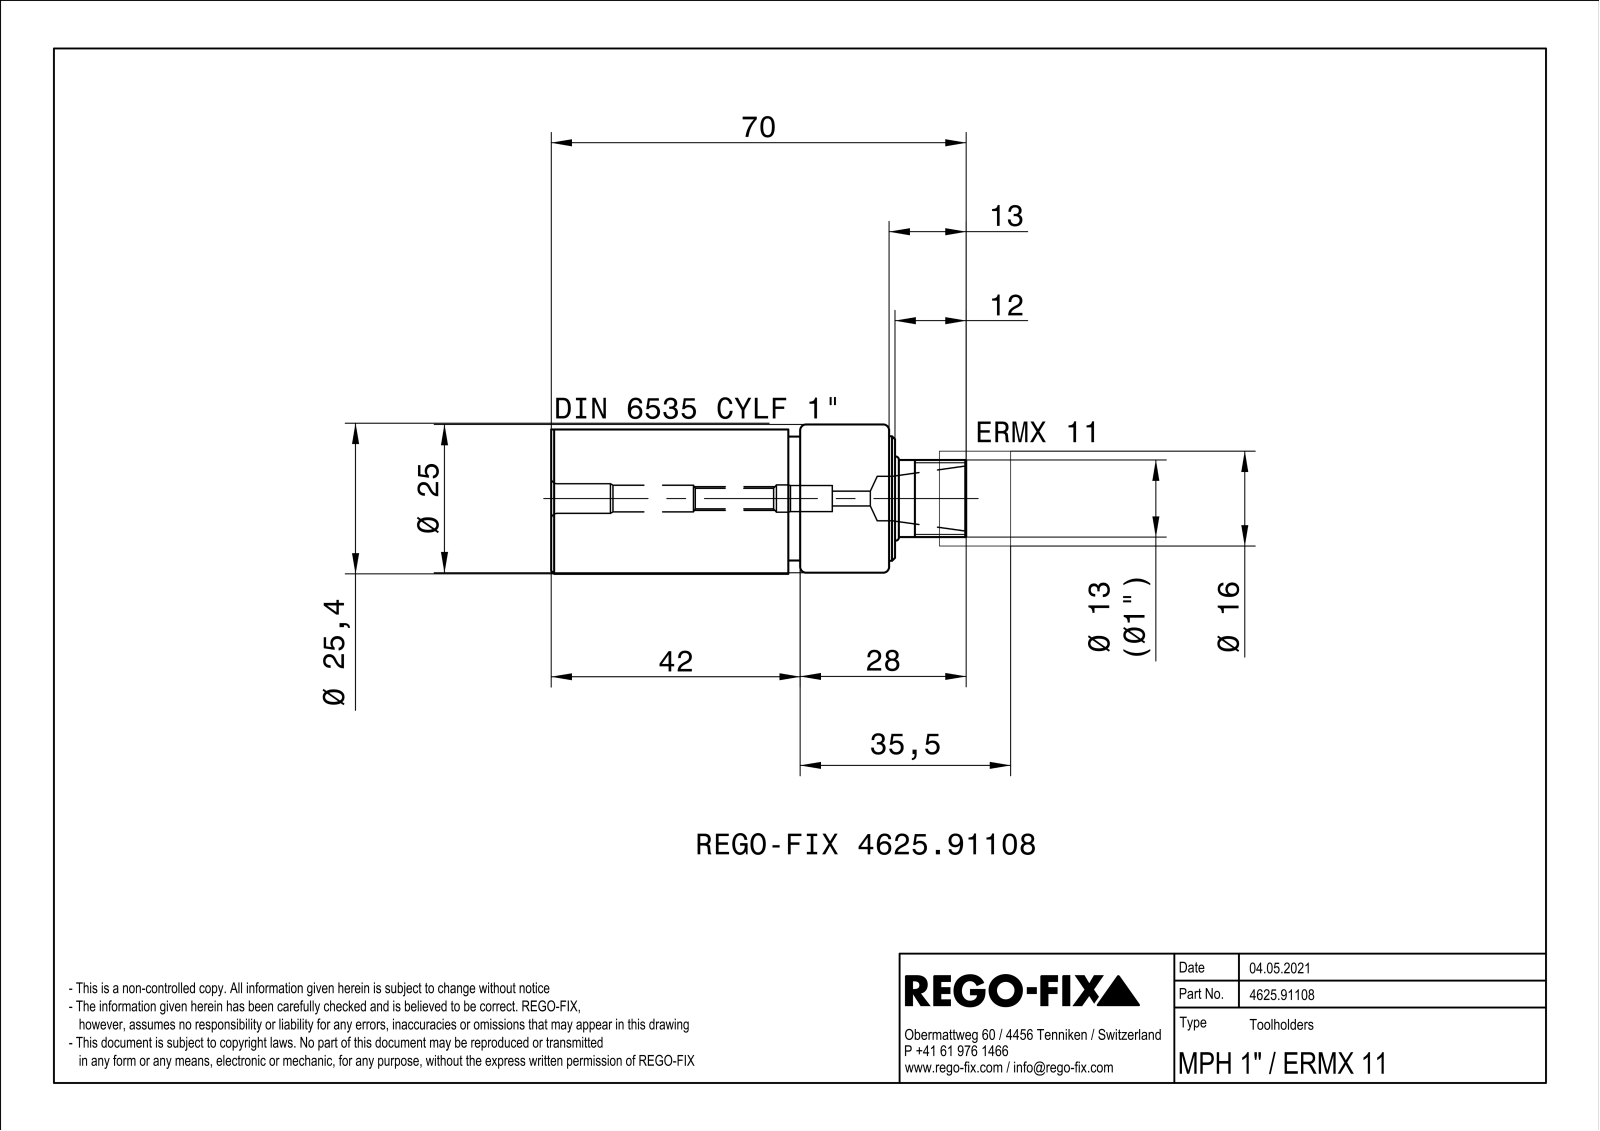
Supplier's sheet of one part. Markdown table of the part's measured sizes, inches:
| quantity | value |
| --- | --- |
| part name | NOCUT |
| STEP written by | SIEMENS PLM Software Solid Edge ST10 (AUTOMOTIVE_DESIGN) |
| units | inches |
| bodies | 1 solid, 86 faces (20 planar, 29 cylindrical, 37 other) |
| overall size | 2.756 × 1 × 0.992 |
| volume | 1.631 in³ |
| surface area | 14.71 in² |
| round holes (diameter × count) | 0.098 × 4, 0.098 × 2, 0.079 × 1, 0.136 × 1, 0.173 × 1, 0.177 × 1, 0.181 × 1, 0.197 × 1, 0.295 × 1, 0.551 × 1, 0.571 × 1, 0.823 × 1 |
| round bosses / shafts (diameter × count) | 1 × 1, 0.984 × 1, 0.827 × 1, 0.787 × 1, 0.512 × 1, 0.5 × 1, 0.138 × 1 |
| main face-to-face distances | 1.89, 0.118, 0.039, 0.591, 0.236, 0.098, 1.988, 0.276, 0.177, 2.165 |
| hole center spacings | 0.335, 0.473, 0.669 |
